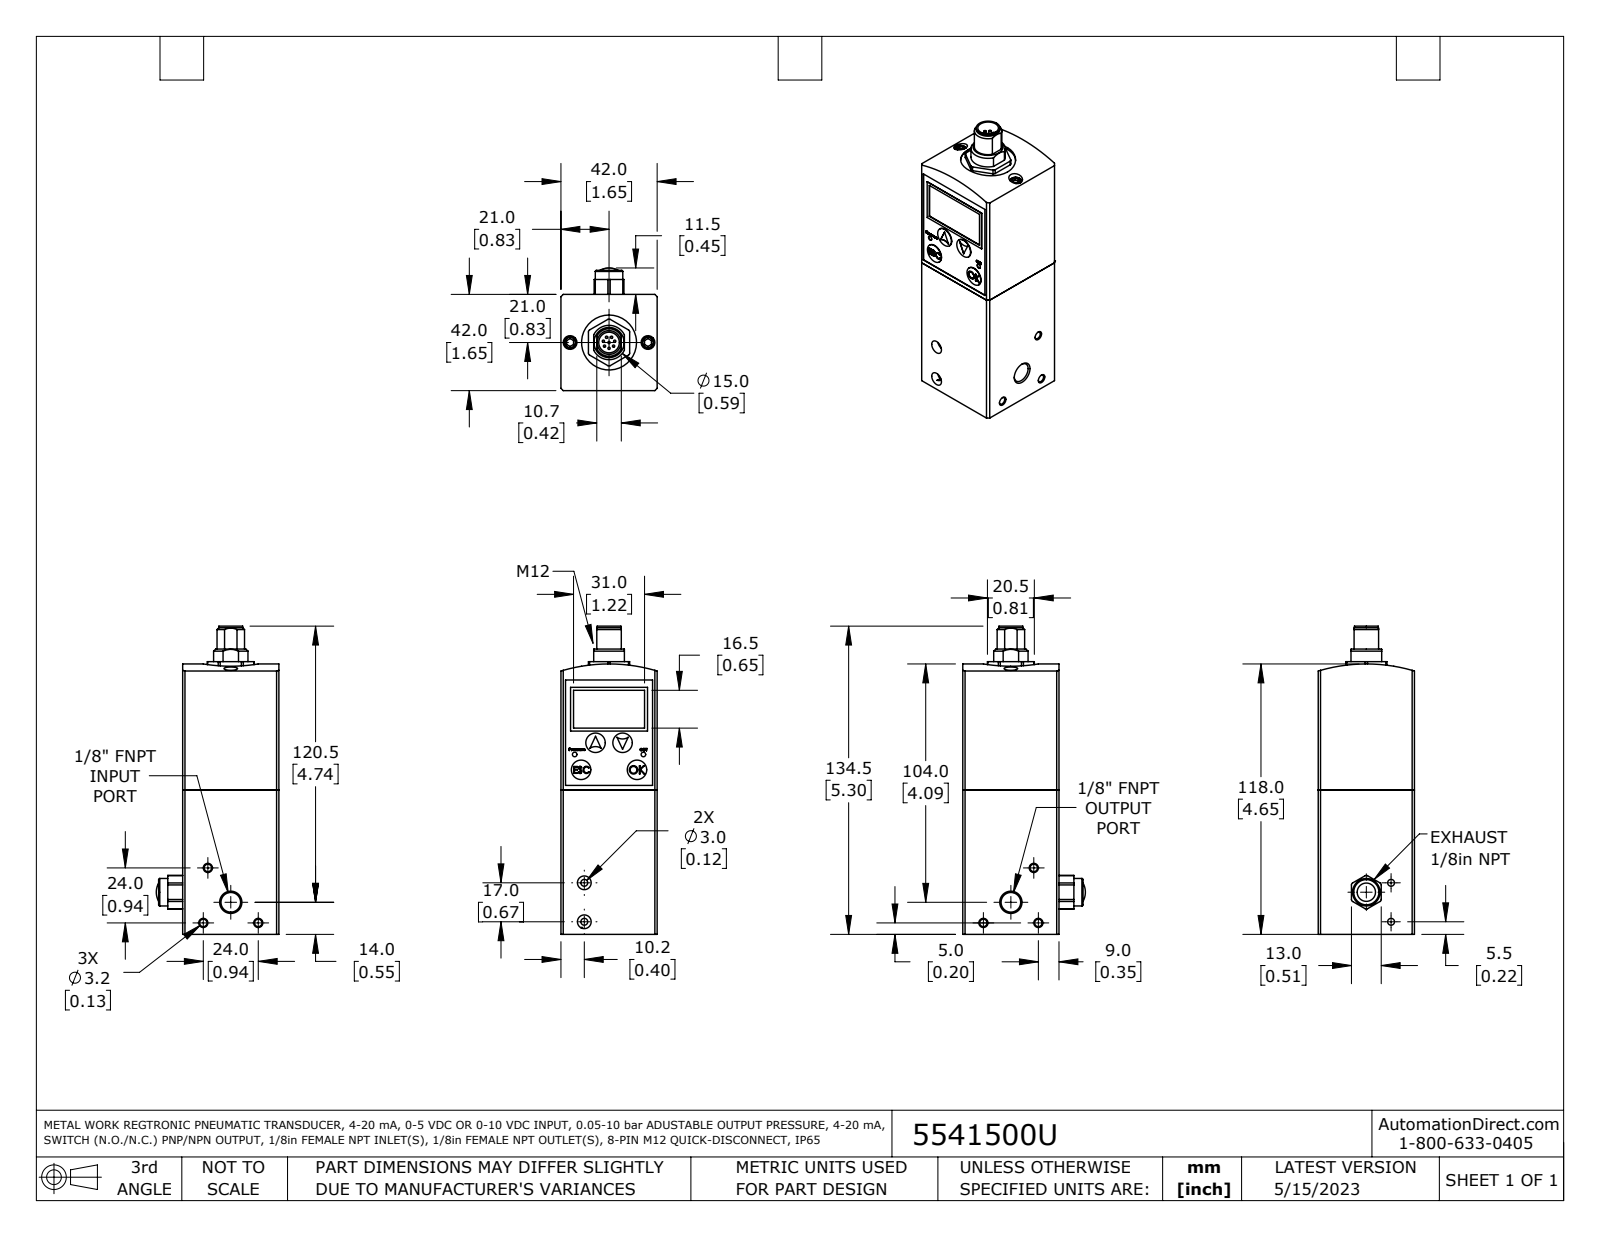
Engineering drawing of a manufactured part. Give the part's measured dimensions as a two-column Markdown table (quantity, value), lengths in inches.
| quantity | value |
| --- | --- |
| part name | 5541500U |
| STEP written by | SolidWorks 2021 (AUTOMOTIVE_DESIGN) |
| units | inches |
| bodies | 1 solid, 538 faces (243 planar, 248 cylindrical, 47 other) |
| overall size | 5.295 × 2.107 × 1.654 |
| volume | 12.61 in³ |
| surface area | 41.89 in² |
| round holes (diameter × count) | 0.236 × 8, 0.128 × 3, 0.03 × 2, 0.079 × 2, 0.118 × 2, 0.041 × 1, 0.145 × 1, 0.337 × 1, 0.354 × 1, 0.945 × 1 |
| round bosses / shafts (diameter × count) | 0.039 × 8, 0.197 × 6, 0.335 × 4, 0.023 × 2, 0.472 × 1, 0.409 × 1, 0.117 × 1, 0.033 × 1 |
| partial cylindrical surfaces (radius × count) | 0.039 × 12, 0.006 × 4, 0.009 × 3, 0.004 × 2, 0.004 × 2, 0.005 × 2, 0.005 × 2, 0.007 × 2 |
| main face-to-face distances | 1.654, 1.646, 0.016, 1.638, 2.283, 2.48, 1.653, 0.015, 0.079, 0.276 |
| hole center spacings | 0.676, 0.882, 1.413, 0.669, 1.339, 0.591, 1.15, 1.765 |
